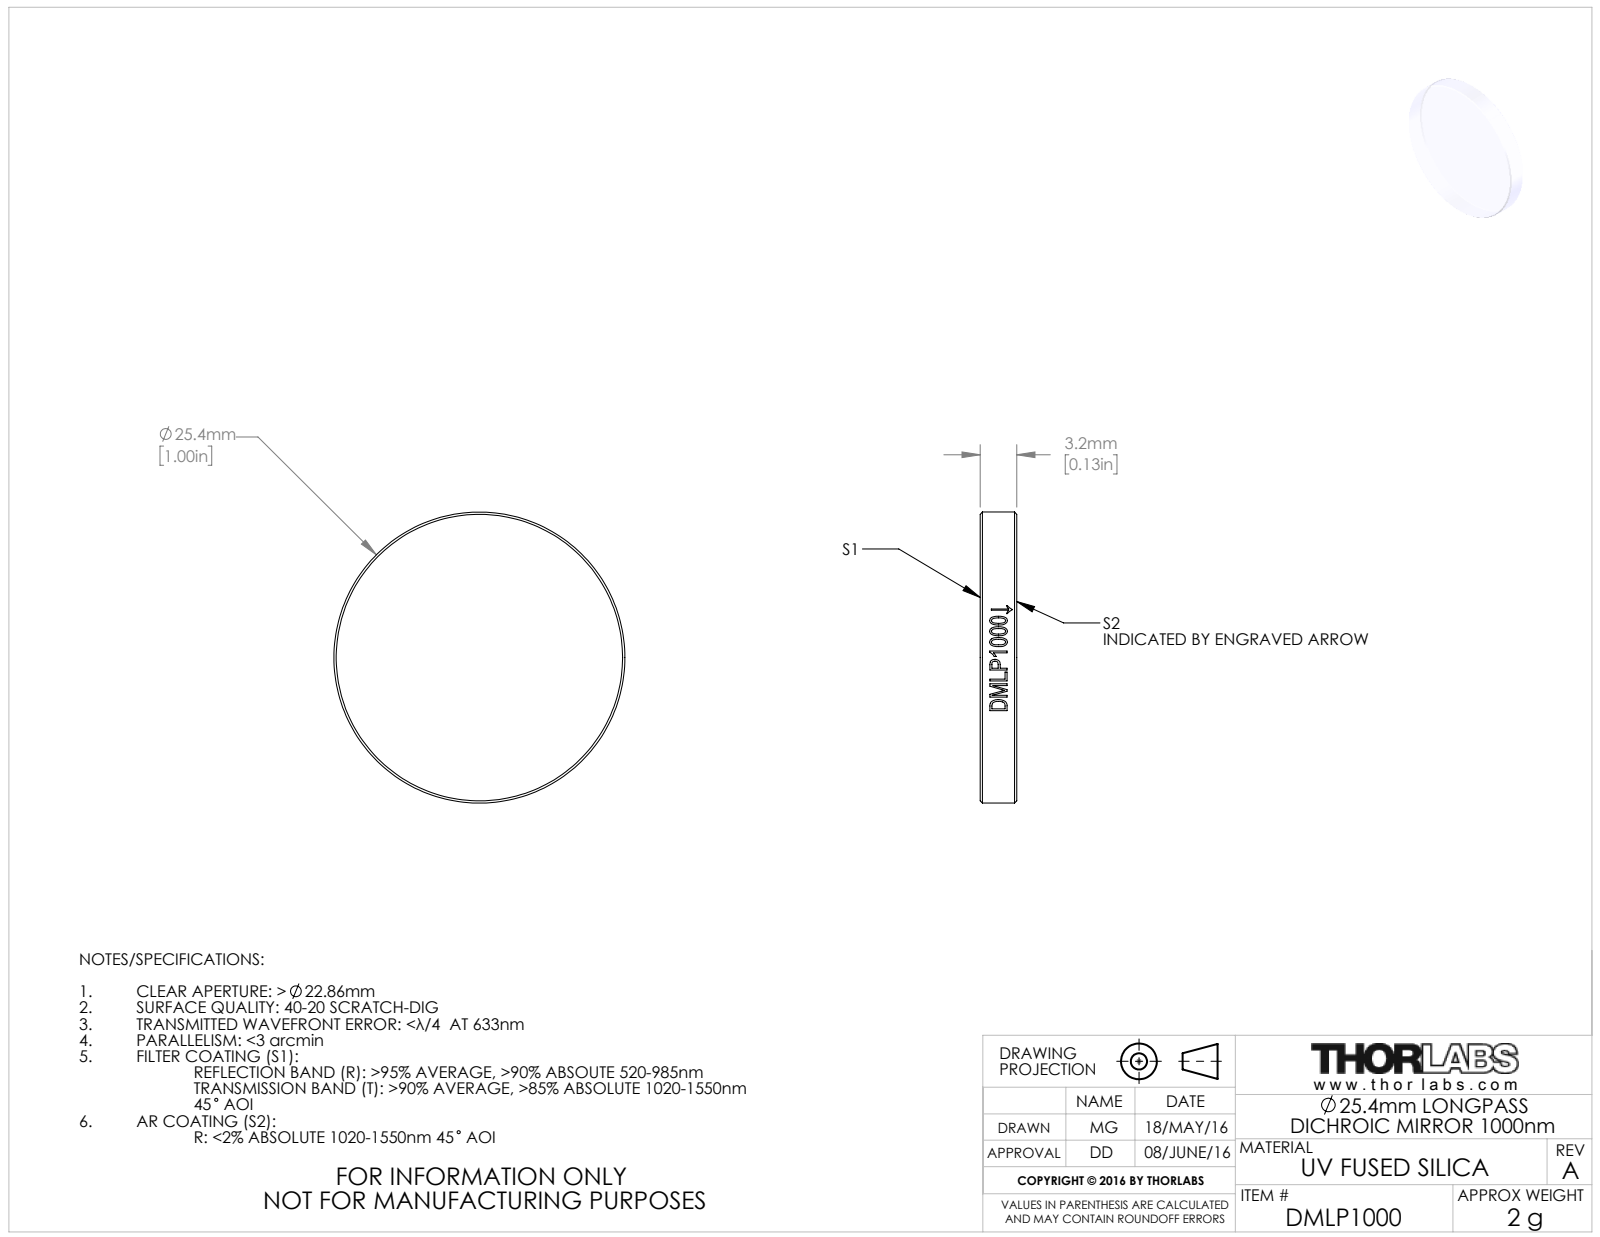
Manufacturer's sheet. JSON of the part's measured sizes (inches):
{"part_name": "TTN045159-E0W", "step_written_by": "SolidWorks 2016 (CONFIG_CONTROL_DESIGN)", "units": "inches", "bodies": {"solids": 1, "faces": 22, "planar": 2, "cylindrical": 16, "other": 4}, "overall_size": [1, 1, 0.126], "volume_in3": 0.099, "surface_area_in2": 1.938, "round_bosses_or_shafts": [[1, 1]], "face_to_face_distances": [0.126]}
